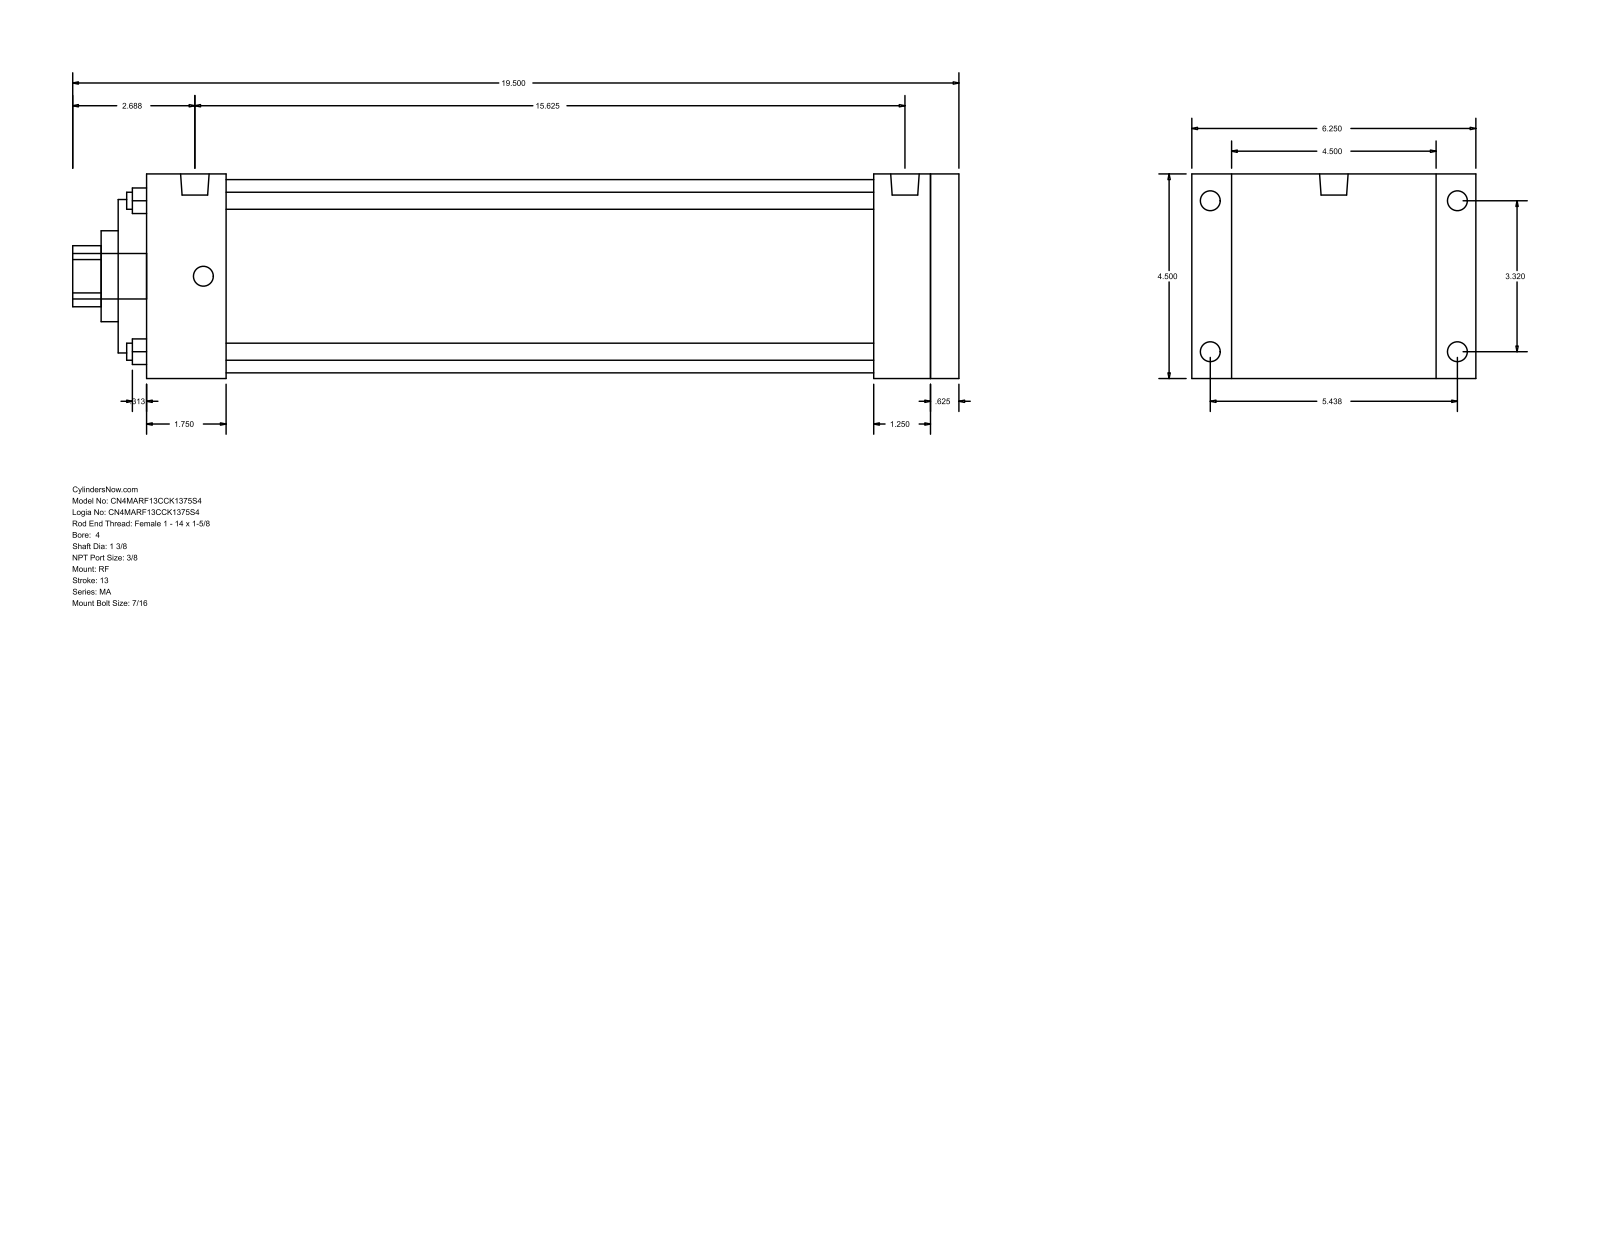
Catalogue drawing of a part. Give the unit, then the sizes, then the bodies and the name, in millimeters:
Units: millimetres
Overall size (bounding box): 495.3 × 158.75 × 114.3
Round holes (diameter × count): ⌀9.53 ×4, ⌀34.92 ×1, ⌀50.8 ×1, ⌀85.72 ×1, ⌀107.95 ×1
Round bosses / shafts (diameter × count): ⌀11.11 ×8, ⌀15.93 ×2, ⌀25.4 ×1
Partial cylindrical surfaces — rounded edges, fillets, slot ends (radius × count): R17.06 ×1
Main face-to-face distances: 114.3, 454.03, 15.87, 438.16, 469.9, 22.23, 136.53, 422.28, 406.41, 31.75
Hole centre spacings: 59.62, 84.32, 119.25
Bodies: 0 solids, 94 faces (65 planar, 29 cylindrical, 0 other)
Part name (STEP PRODUCT): MA_RF__0400_1.375
STEP written by: GSSL Pune (CONFIG_CONTROL_DESIGN)
